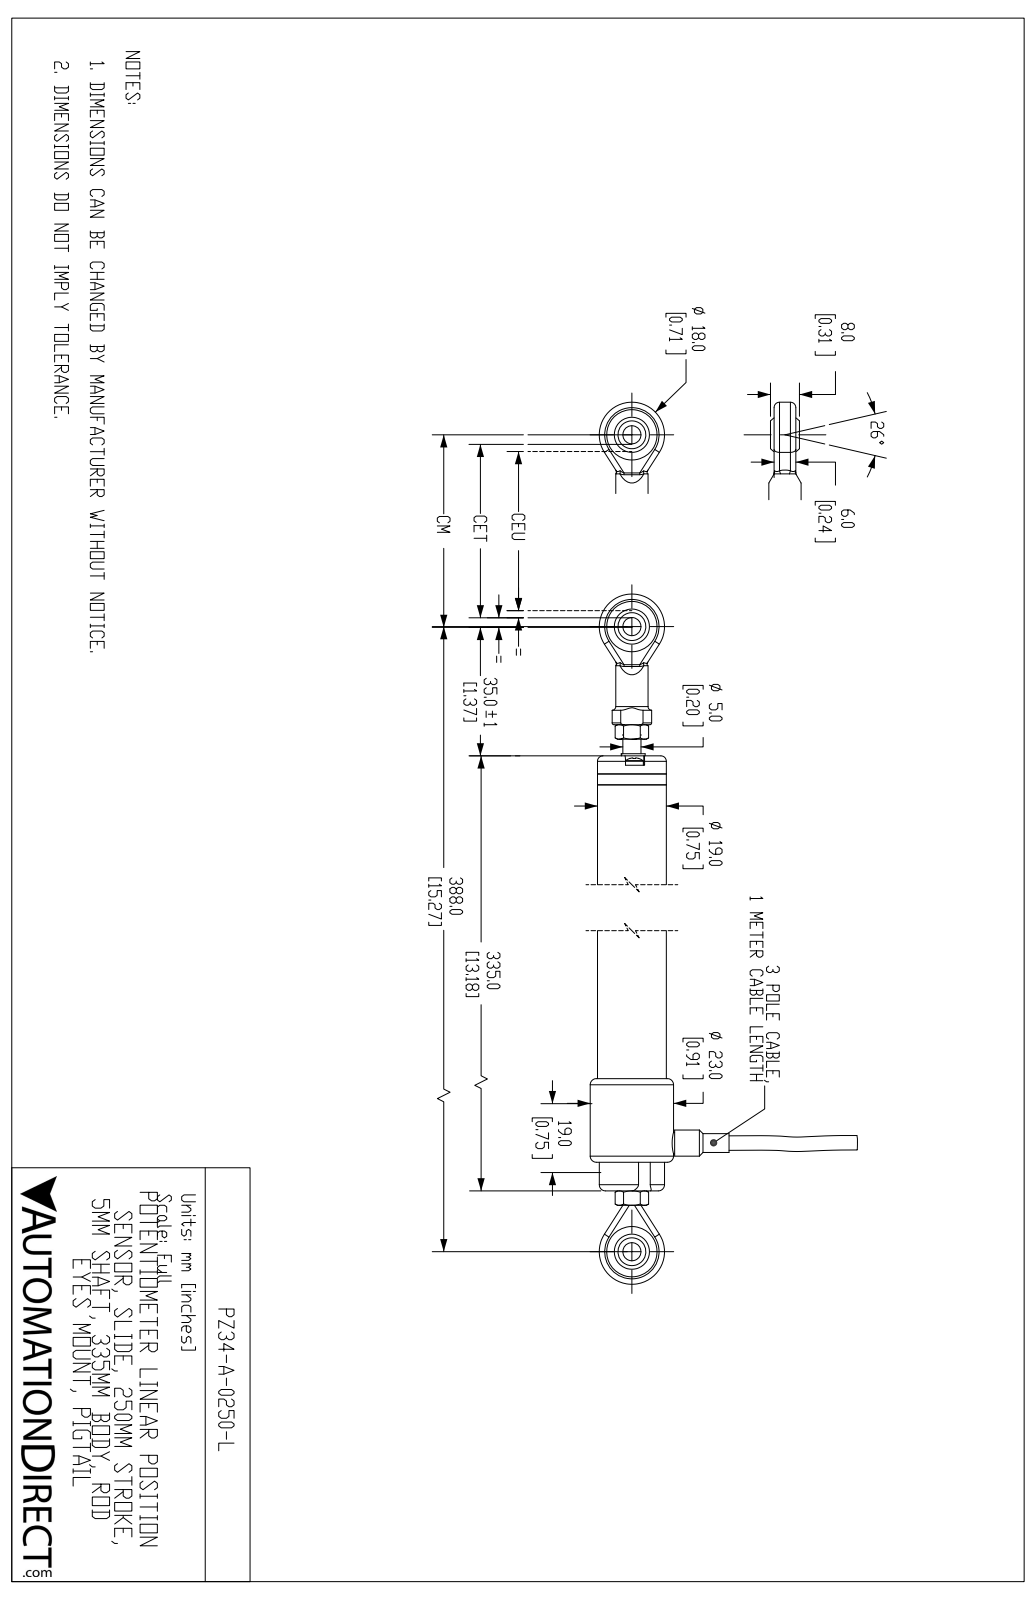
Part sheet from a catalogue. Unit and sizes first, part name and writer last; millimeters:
Units: millimetres
Overall size (bounding box): 405.5 × 73.8 × 23
Round holes (diameter × count): ⌀2 ×4, ⌀2.9 ×4, ⌀5 ×2, ⌀5.3 ×2, ⌀13.9 ×2, ⌀3.5 ×1, ⌀4.2 ×1, ⌀6.1 ×1, ⌀9 ×1, ⌀19.1 ×1
Round bosses / shafts (diameter × count): ⌀5 ×5, ⌀2.5 ×4, ⌀23 ×1, ⌀19 ×1, ⌀18 ×1, ⌀8.9 ×1, ⌀7.2 ×1, ⌀6 ×1
Partial cylindrical surfaces — rounded edges, fillets, slot ends (radius × count): R1.5 ×8, R0.3 ×4, R0.5 ×2, R1 ×2, R2.6 ×2, R9 ×2, R0.4 ×1, R1.6 ×1
Main face-to-face distances: 312, 309, 3, 8, 5.7, 5.4, 5.5, 1.3, 1, 6.7
Hole centre spacings: 6.8, 2.1, 13.5, 13.7, 387.5
Volume: 110 500 mm³ · Surface area: 37 700 mm²
Bodies: 18 solids, 916 faces (334 planar, 198 cylindrical, 384 other)
Part name (STEP PRODUCT): PZ34-A-0250-L
STEP written by: SolidWorks 2019 (AUTOMOTIVE_DESIGN)
